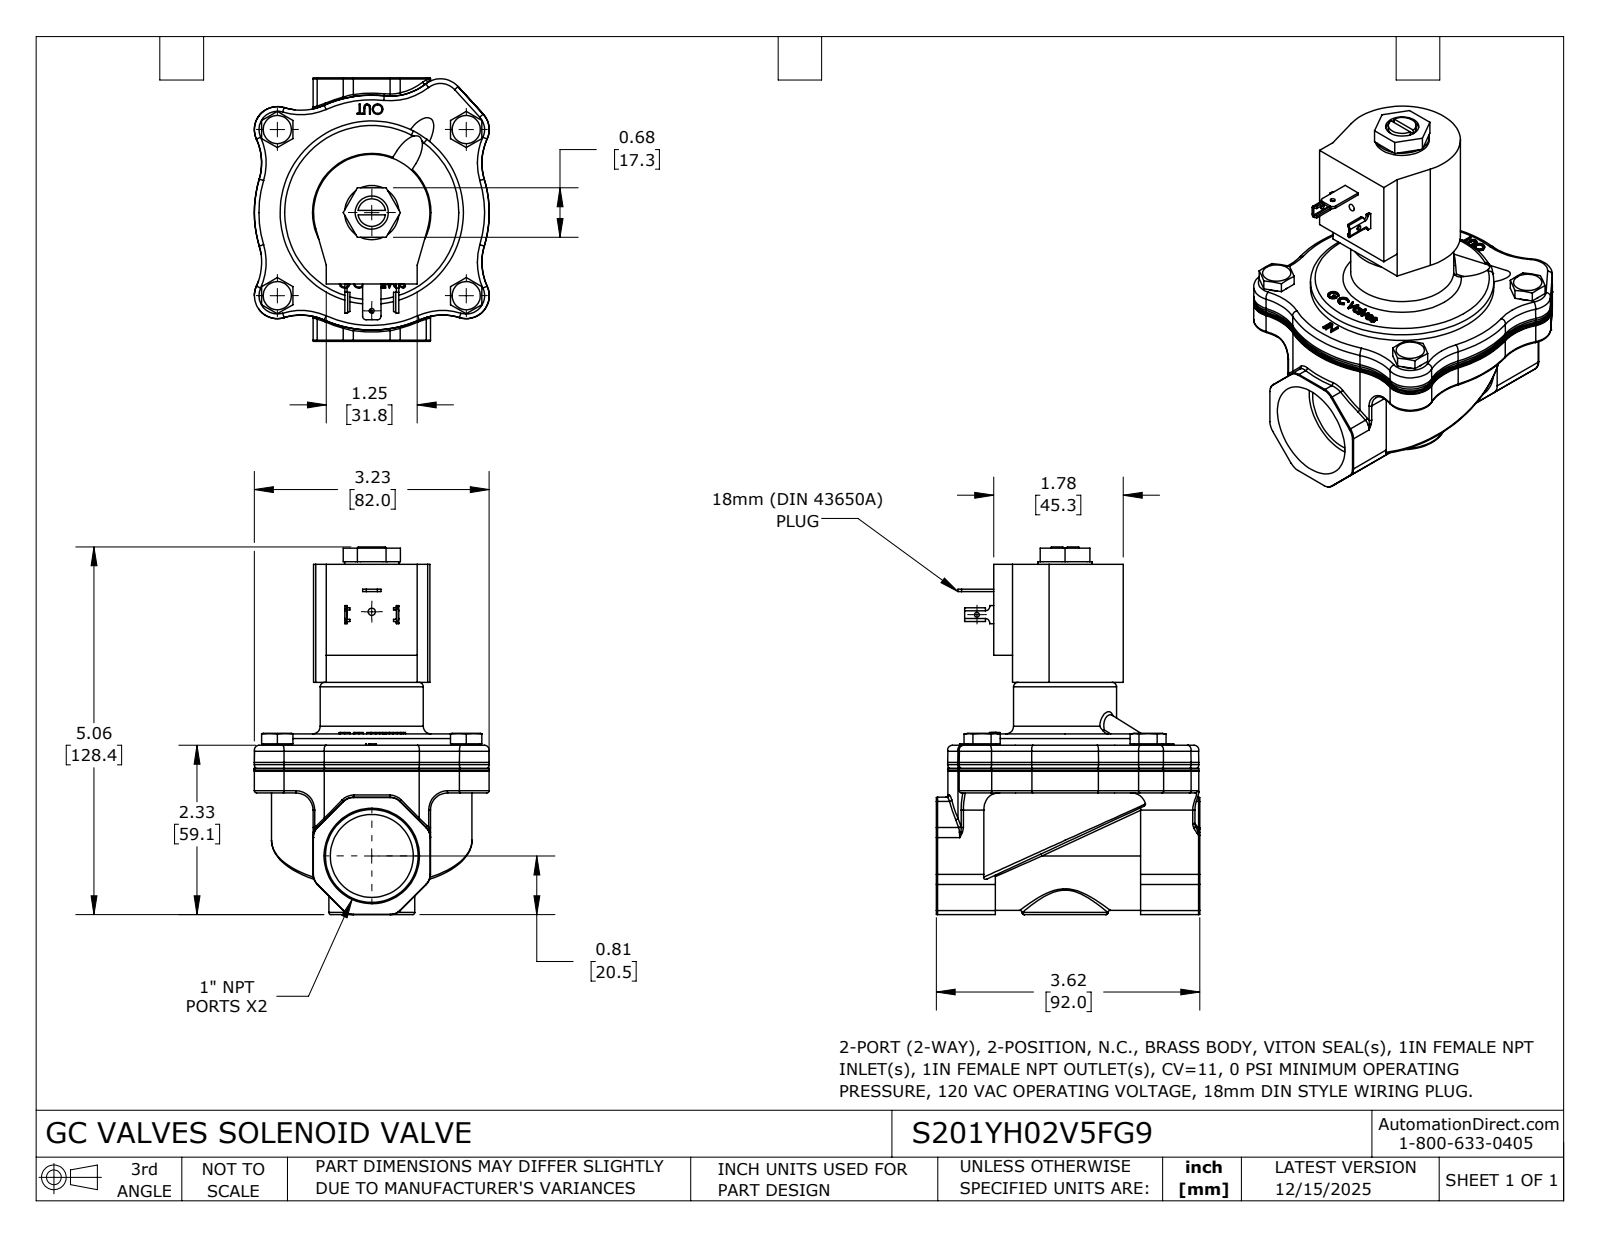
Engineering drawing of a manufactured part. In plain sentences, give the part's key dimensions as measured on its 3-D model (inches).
The part is named "S201YH02V5FG9". Its 3-D file was written by "SolidWorks 2024 (CONFIG_CONTROL_DESIGN)". It is 1 solid with 671 faces: 220 planar, 172 cylindrical and 279 other. Overall it measures 5.055 by 3.622 by 3.232 inches. Its volume is 19.13 cubic inches and its surface area 70.49 square inches. Round holes: 1 of diameter 0.066, 1 of diameter 0.067, 1 of diameter 0.1, 1 of diameter 0.456, 1 of diameter 1.141. Round bosses or shafts: 4 of diameter 0.388, 1 of diameter 2.52, 1 of diameter 1.417, 1 of diameter 1.181, 1 of diameter 0.746, 1 of diameter 0.38. Partial cylindrical surfaces (rounded edges, fillets, slot ends): 24 of radius 0.031, 24 of radius 0.787, 12 of radius 0.315, 8 of radius 0.197, 4 of radius 0.006, 4 of radius 0.041, 2 of radius 0.05, 2 of radius 0.06. The main face-to-face distances are 0.157, 0.655, 0.812, 3.141, 2.486, 2.329, 2.485, 2.328, 1.673, 4.814. The hole center spacings are 1.35, 3.356.
